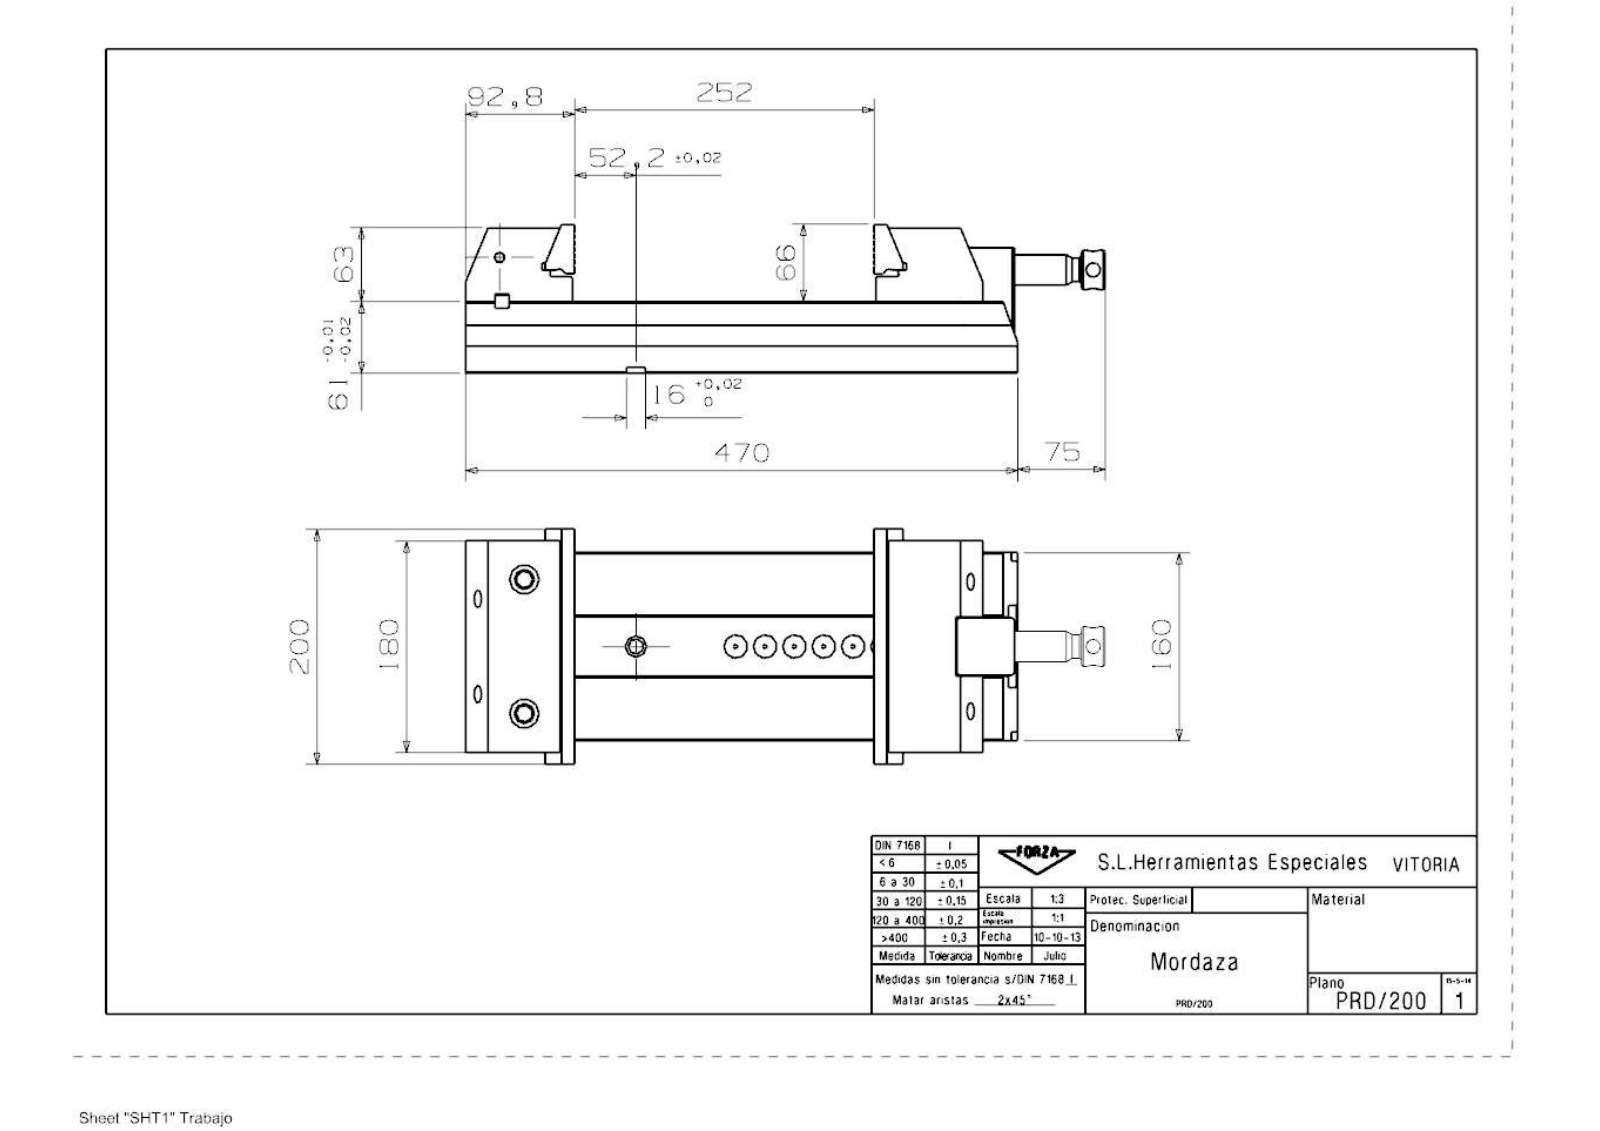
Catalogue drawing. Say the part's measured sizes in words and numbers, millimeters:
The part is named "PRD_200_Mordaza". Its 3-D file was written by "SIEMENS PLM Software NX 9.0 (CONFIG_CONTROL_DESIGN)". It is 11 solids with 464 faces: 280 planar, 126 cylindrical and 58 other. Overall it measures 544.42 by 200 by 126.95 millimeters. Its volume is 5 527 000 cubic millimeters and its surface area 589 565 square millimeters. Round holes: 6 of diameter 15, 5 of diameter 5.19, 5 of diameter 13, 4 of diameter 6.99, 4 of diameter 8.5, 4 of diameter 10, 3 of diameter 8.78, 3 of diameter 10.58, 3 of diameter 19, 2 of diameter 12, 2 of diameter 12.38, 2 of diameter 14.38. Round bosses or shafts: 1 of diameter 34, 1 of diameter 33.8, 1 of diameter 26, 1 of diameter 20, 1 of diameter 16.5. Partial cylindrical surfaces (rounded edges, fillets, slot ends): 24 of radius 0.4, 4 of radius 8, 4 of radius 20, 2 of radius 1.6, 2 of radius 6, 2 of radius 7, 1 of radius 4, 1 of radius 9. The main face-to-face distances are 61, 29.2, 31.8, 124, 94.8, 63, 10, 45, 160, 55. The hole center spacings are 14.5, 95.5, 81, 110, 16.47, 16.55, 24.52, 30.
